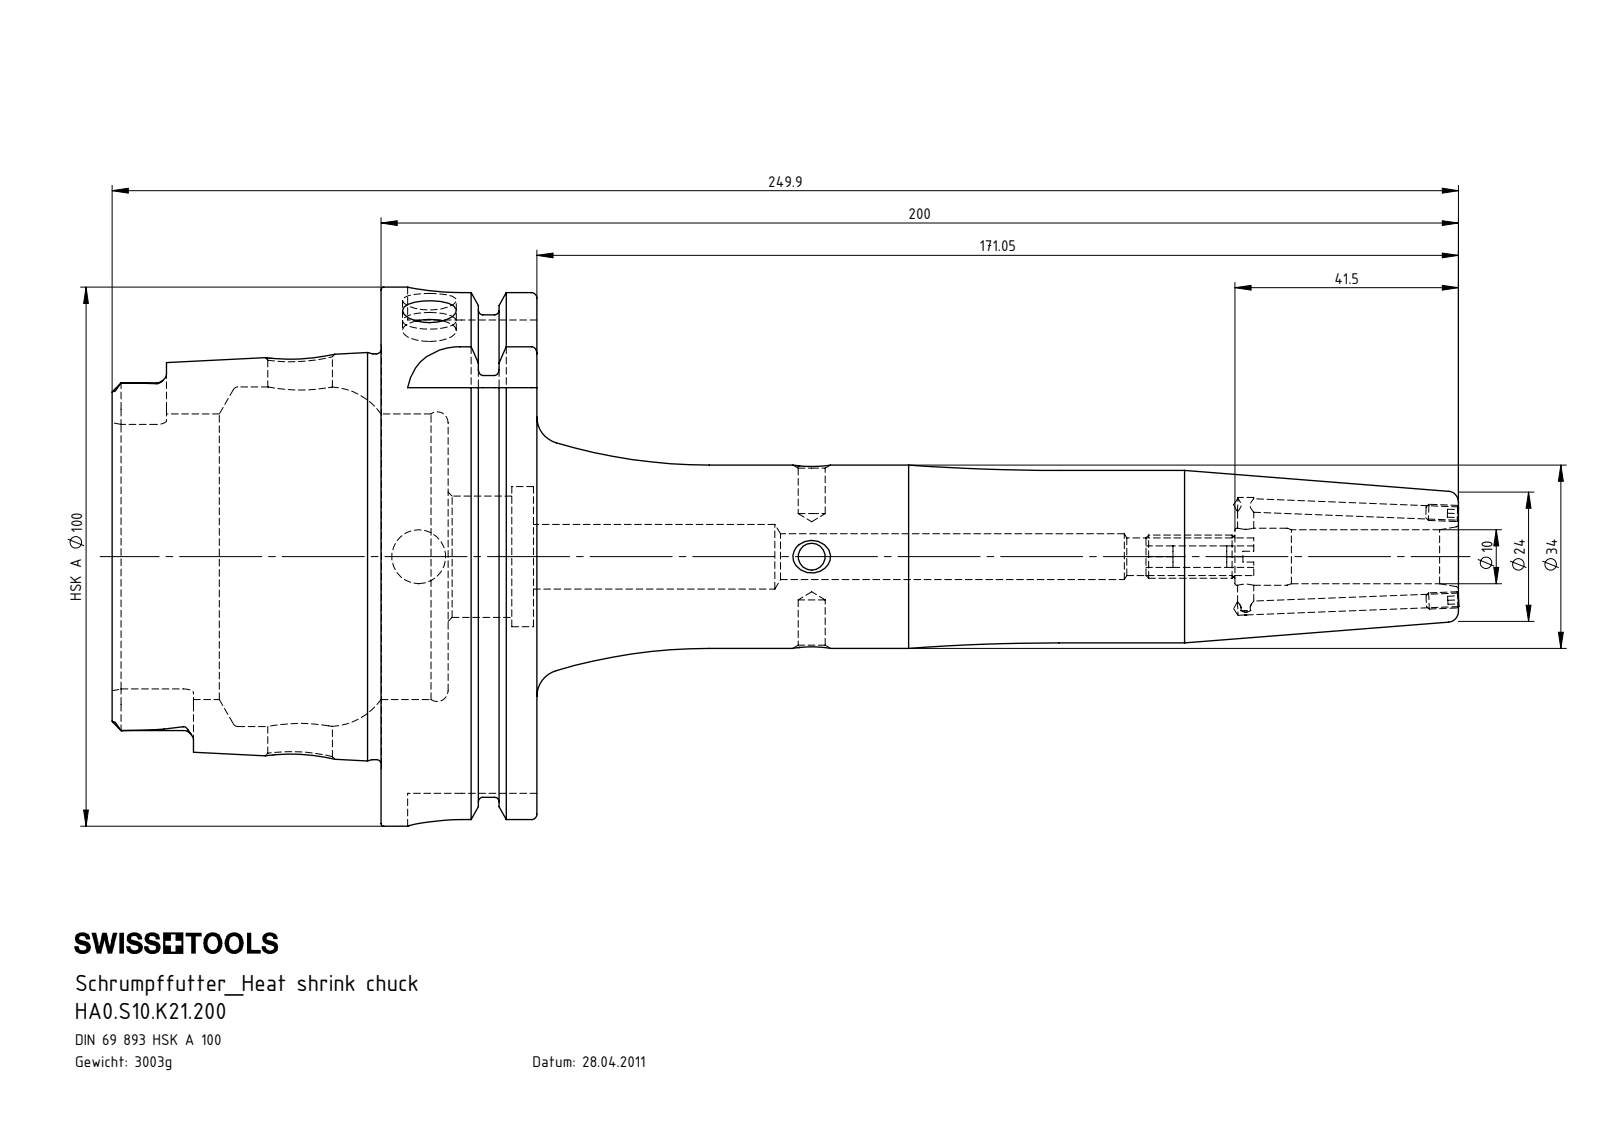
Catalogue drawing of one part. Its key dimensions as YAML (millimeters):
part_name: "ERU-AN3.K01.020_A; HA0.S10.K21.200; ERU-CJ2.001.006; HA0-S10.K21.200_C_Fertigbearbeitung"
step_written_by: "SolidWorks 2017 (CONFIG_CONTROL_DESIGN)"
units: millimeters
bodies: {solids: 4, faces: 305, planar: 95, cylindrical: 88, other: 122}
overall_size: [249.98, 100, 100]
volume: 382540
surface_area: 73350
round_holes:
  - {diameter: 10, count: 4}
  - {diameter: 2.5, count: 2}
  - {diameter: 5, count: 2}
  - {diameter: 12, count: 2}
  - {diameter: 3, count: 1}
  - {diameter: 4, count: 1}
  - {diameter: 7, count: 1}
  - {diameter: 8.5, count: 1}
  - {diameter: 10.6, count: 1}
  - {diameter: 22.5, count: 1}
  - {diameter: 26, count: 1}
  - {diameter: 53, count: 1}
round_bosses_or_shafts:
  - {diameter: 3, count: 2}
  - {diameter: 100, count: 1}
  - {diameter: 91.95, count: 1}
  - {diameter: 75.26, count: 1}
  - {diameter: 34, count: 1}
  - {diameter: 32, count: 1}
  - {diameter: 8, count: 1}
partial_cylinders:
  - {radius: 1.9, count: 6}
  - {radius: 4.88, count: 4}
  - {radius: 10, count: 4}
face_to_face_distances: [28.95, 16.5, 12.45, 49.9, 62.35, 78.85, 87.8, 78.2, 28.3, 15.85]
hole_center_spacings: [72.95, 80.55, 94.95, 175.5]
